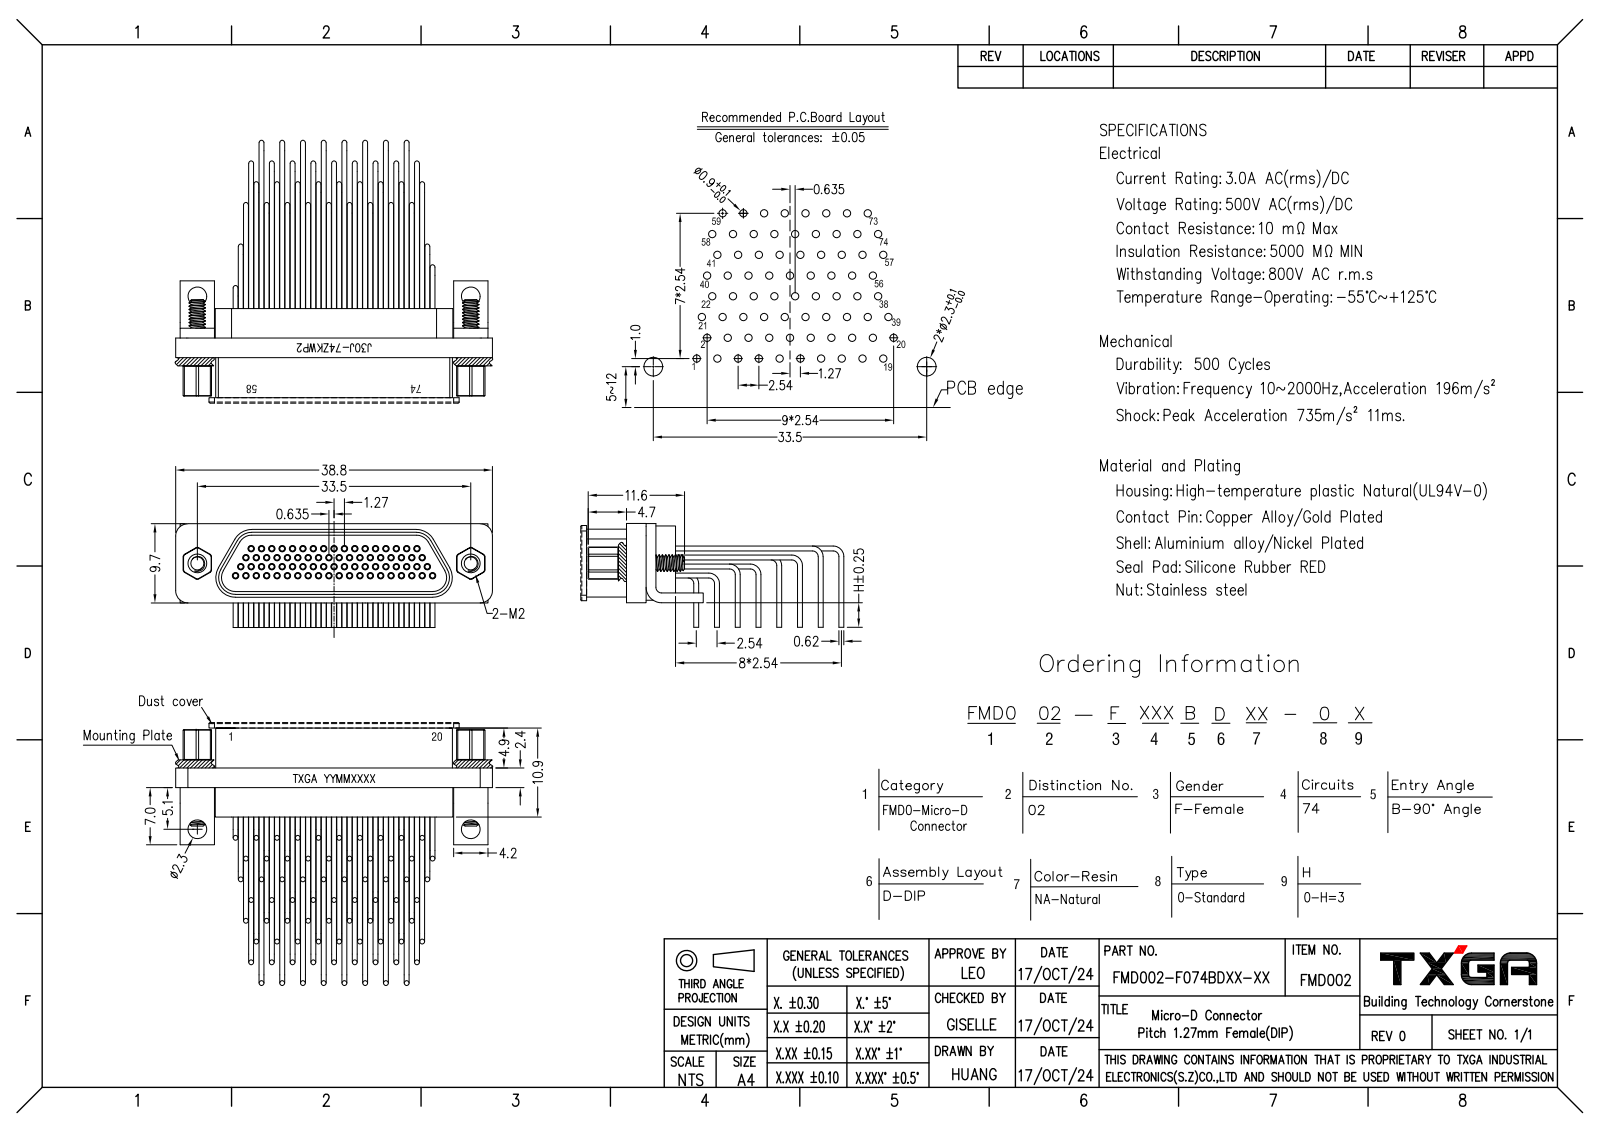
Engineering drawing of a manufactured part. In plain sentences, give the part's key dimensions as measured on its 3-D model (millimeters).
The part is named "FMD002-F074BDNA-00". Its 3-D file was written by "SolidWorks 2021 (CONFIG_CONTROL_DESIGN)". It is 1 solid with 2140 faces: 786 planar, 752 cylindrical and 602 other. Overall it measures 38.8 by 31.52 by 12.7 millimeters. Its volume is 2 735 cubic millimeters and its surface area 6 095 square millimeters. Round holes: 74 of diameter 0.6, 2 of diameter 1.6, 2 of diameter 1.8, 2 of diameter 2.3, 2 of diameter 3.2. Round bosses or shafts: 74 of diameter 0.8, 74 of diameter 0.6, 2 of diameter 2. Partial cylindrical surfaces (rounded edges, fillets, slot ends): 12 of radius 0.3, 4 of radius 1.5, 4 of radius 1.7, 4 of radius 2, 4 of radius 2.4, 1 of radius 0.7, 1 of radius 1.9. The main face-to-face distances are 0.7, 8.3, 6, 1.4, 0.4, 7.6, 1.1, 9.4, 8, 8.7. The hole center spacings are 1.27, 3.36, 2.2, 2.54, 3.81, 5.08, 4.58, 6.35.
